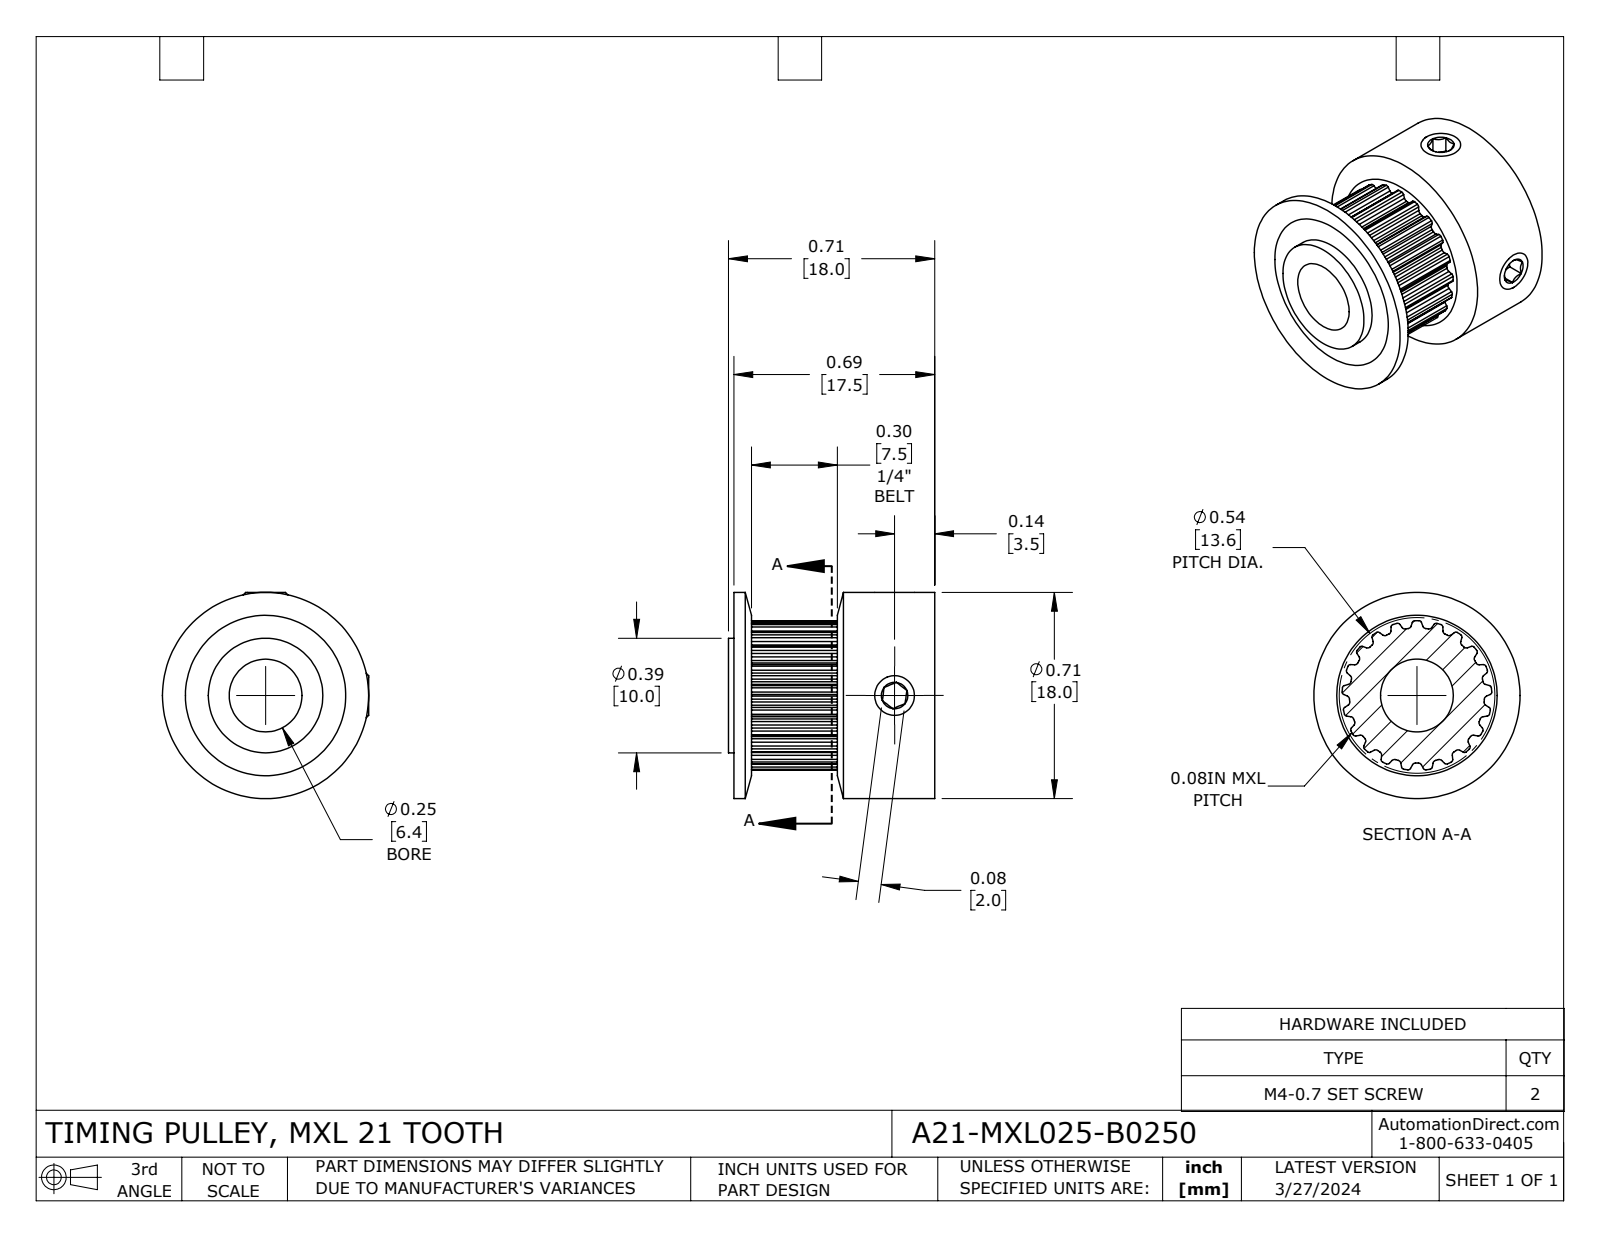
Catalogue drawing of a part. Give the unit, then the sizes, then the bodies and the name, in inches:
Units: inches
Overall size (bounding box): 0.709 × 0.709 × 0.709
Round holes (diameter × count): ⌀0.13 ×2, ⌀0.25 ×1
Round bosses / shafts (diameter × count): ⌀0.157 ×2, ⌀0.709 ×1, ⌀0.394 ×1
Partial cylindrical surfaces — rounded edges, fillets, slot ends (radius × count): R0.009 ×42, R0.012 ×42, R0.232 ×1, R0.257 ×1
Main face-to-face distances: 0.039, 0.669, 0.335, 0.709, 0.079, 0.63, 0.374, 0.295, 0.118
Volume: 0.169 in³ · Surface area: 3.469 in²
Bodies: 3 solids, 252 faces (63 planar, 157 cylindrical, 32 other)
Part name (STEP PRODUCT): A21-MXL025-B0250
STEP written by: SolidWorks 2021 (CONFIG_CONTROL_DESIGN)
